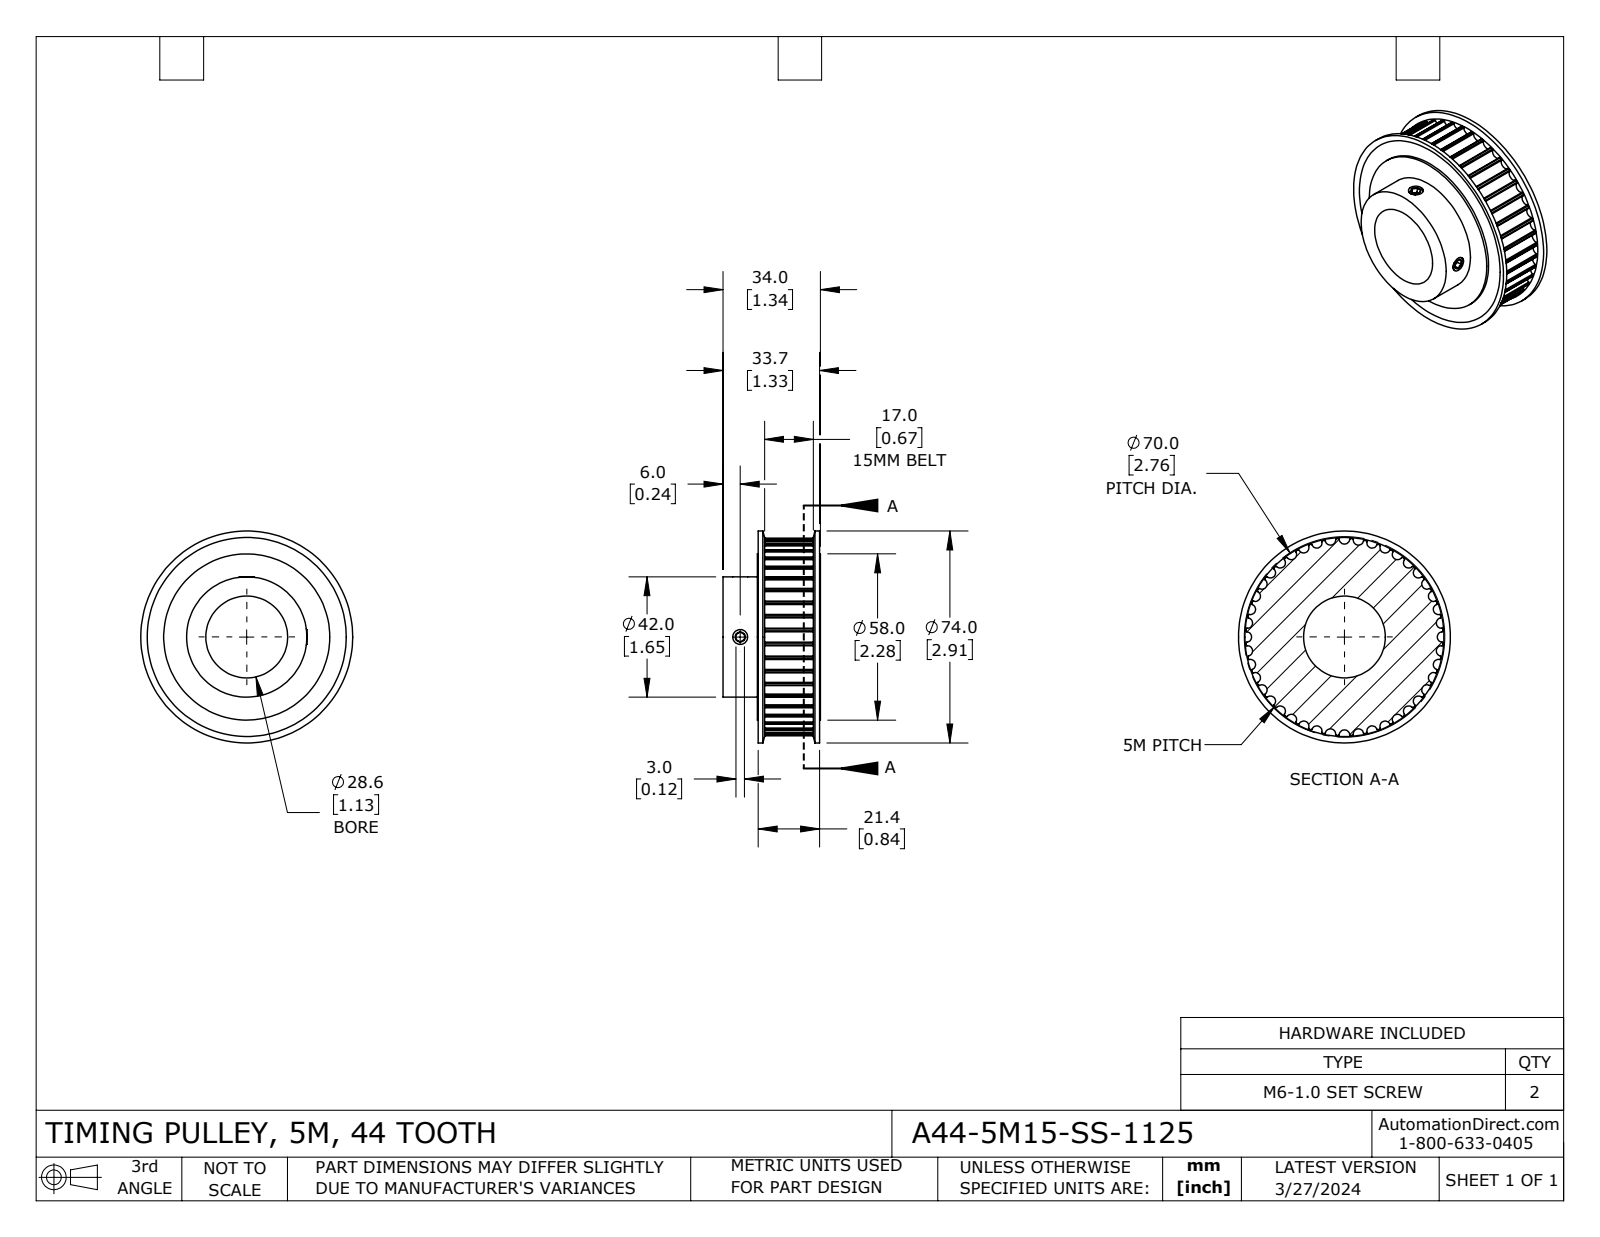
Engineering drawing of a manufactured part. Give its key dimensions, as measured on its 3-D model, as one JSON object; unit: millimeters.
{"part_name": "A44-5M15-SS-1125", "step_written_by": "SolidWorks 2021 (CONFIG_CONTROL_DESIGN)", "units": "millimeters", "bodies": {"solids": 5, "faces": 302, "planar": 25, "cylindrical": 243, "other": 34}, "overall_size": [74, 74, 34], "volume_mm3": 72245, "surface_area_mm2": 24923, "round_holes": [[5, 2], [28.58, 1], [58, 1]], "round_bosses_or_shafts": [[6, 2], [74, 1], [42, 1]], "partial_cylinders_radius": [[0.3, 88], [1.82, 44], [34.45, 1]], "face_to_face_distances": [2.5, 19.5, 0.9, 21.1, 1.6, 18.6, 17, 22, 20.2, 34]}
